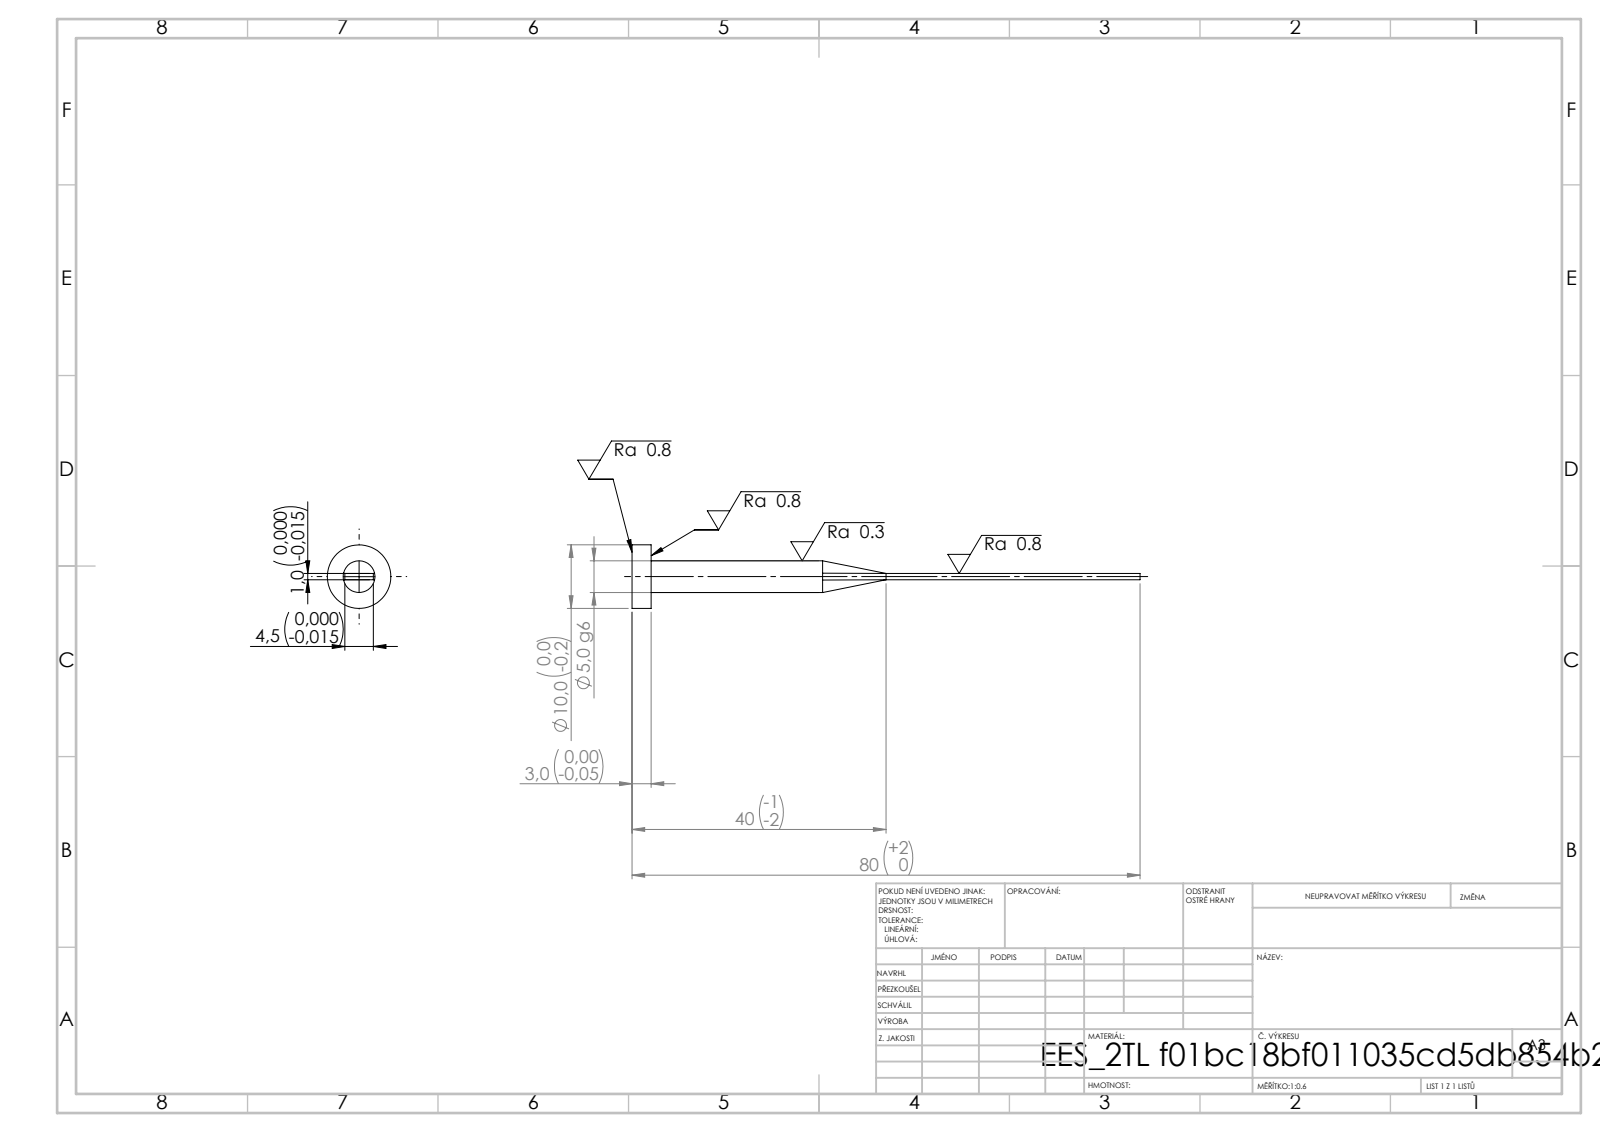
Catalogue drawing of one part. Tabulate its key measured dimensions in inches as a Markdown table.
| quantity | value |
| --- | --- |
| STEP written by | SolidWorks 2019 (CONFIG_CONTROL_DESIGN) |
| units | inches |
| bodies | 1 solid, 15 faces (7 planar, 4 cylindrical, 4 other) |
| overall size | 3.15 × 0.394 × 0.394 |
| volume | 0.065 in³ |
| surface area | 1.905 in² |
| round bosses / shafts (diameter × count) | 0.394 × 1, 0.197 × 1 |
| main face-to-face distances | 0.039, 0.118, 0.177, 3.15, 3.031 |
